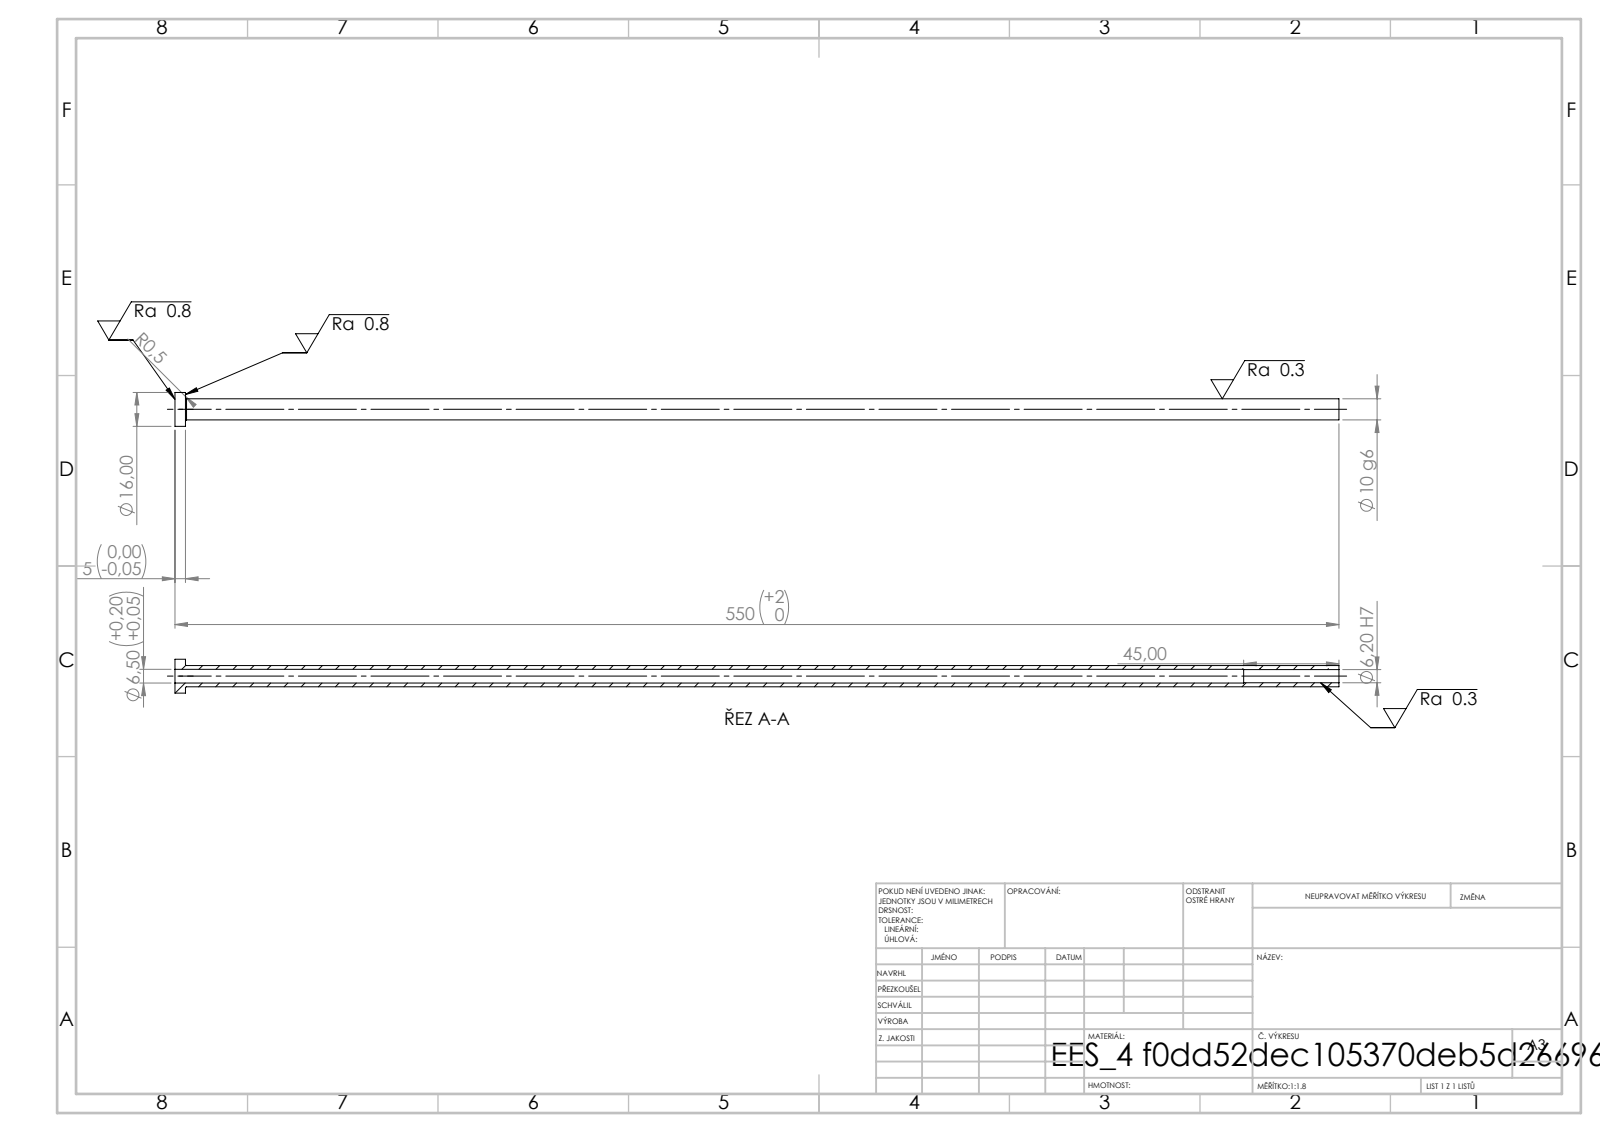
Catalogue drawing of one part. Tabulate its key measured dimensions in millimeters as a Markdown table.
| quantity | value |
| --- | --- |
| STEP written by | SolidWorks 2019 (CONFIG_CONTROL_DESIGN) |
| units | millimeters |
| bodies | 1 solid, 14 faces (4 planar, 8 cylindrical, 2 other) |
| overall size | 550 × 16 × 16 |
| volume | 25 695 mm³ |
| surface area | 28 897 mm² |
| round holes (diameter × count) | 6.2 × 1, 6.5 × 1 |
| round bosses / shafts (diameter × count) | 16 × 1, 10 × 1 |
| main face-to-face distances | 5, 550, 545, 505, 500, 45 |
